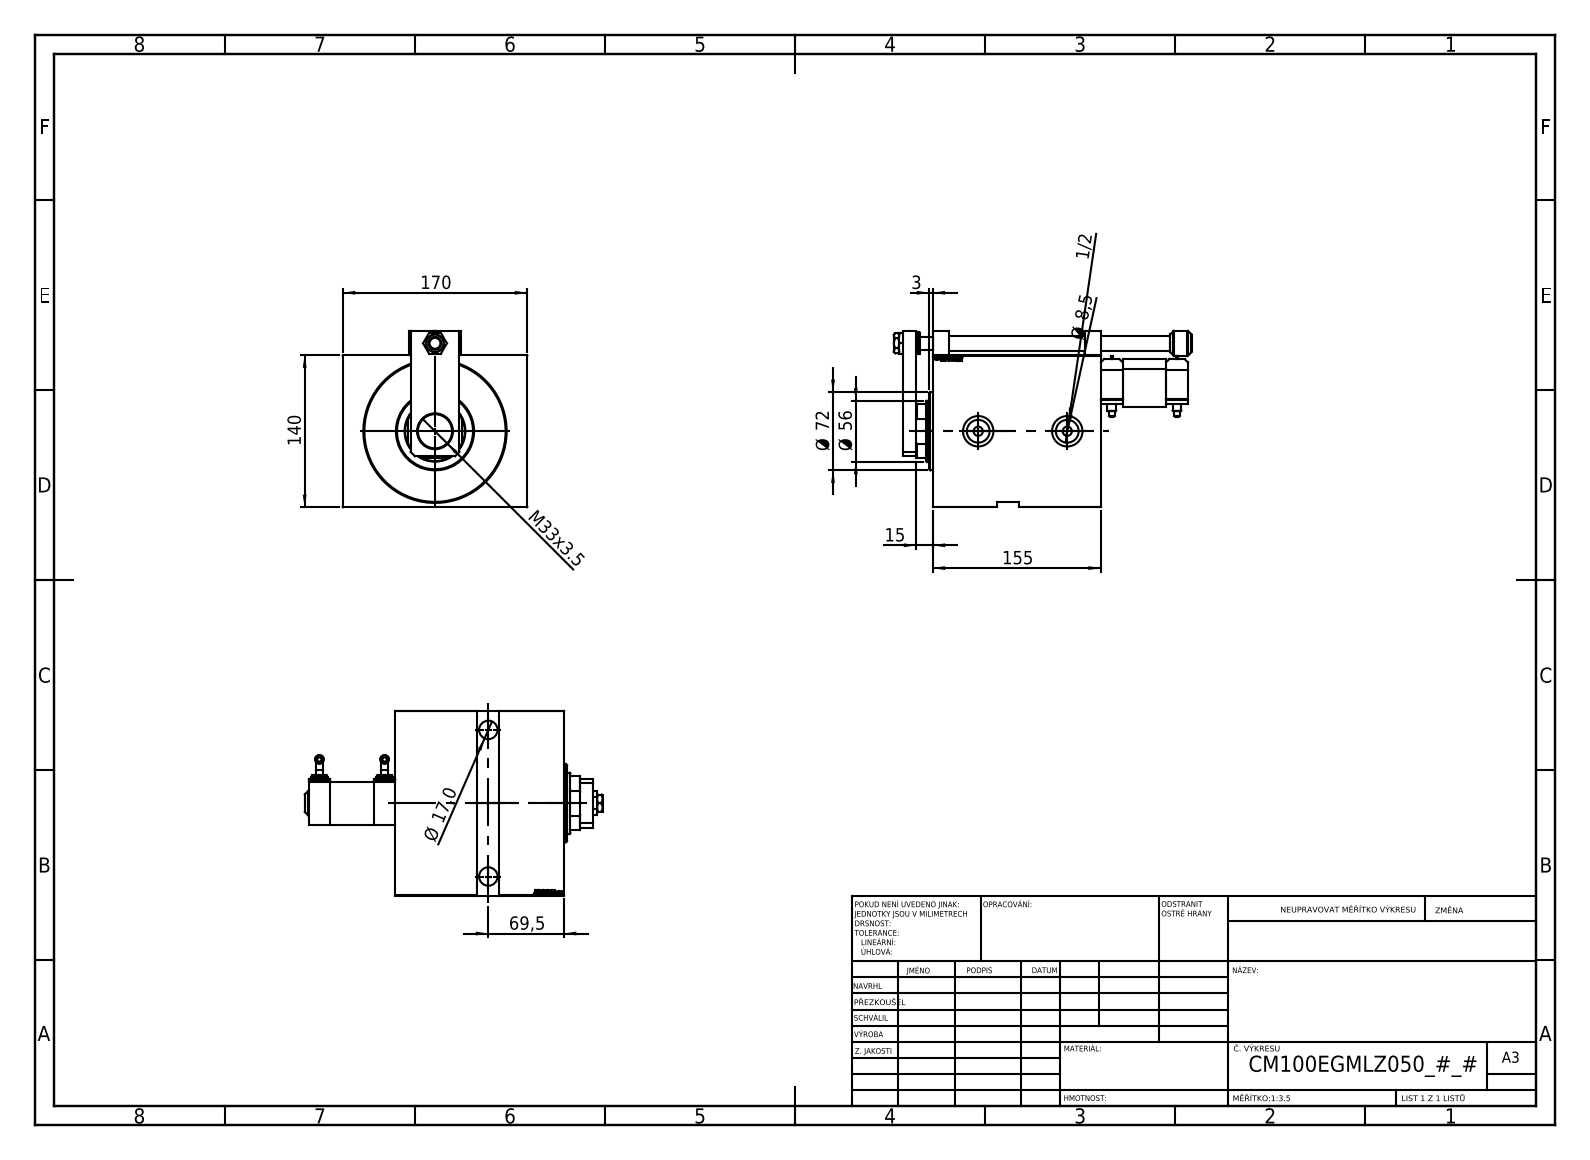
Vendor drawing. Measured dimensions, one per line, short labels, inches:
name: ZARAZKA_P; TYC_P; V450CM_E_Body; NUT_D19_P (+7 more)
written by: SolidWorks 2019 (CONFIG_CONTROL_DESIGN)
unit: in
bodies: 14 solids, 1098 faces (525 planar, 108 cylindrical, 465 other)
size: 10.799 × 6.693 × 6.398
volume: 219 in³; area: 547.6 in²
holes: 4× ⌀0.157, 4× ⌀0.315, 2× ⌀0.335, 2× ⌀0.669, 2× ⌀0.825, 2× ⌀0.984, 2× ⌀1.102, 1× ⌀0.472, 1× ⌀0.512, 1× ⌀0.551, 1× ⌀1.24, 1× ⌀1.299
bosses: 3× ⌀0.787, 2× ⌀0.63, 2× ⌀0.551, 2× ⌀0.315, 2× ⌀0.236, 2× ⌀0.198, 1× ⌀4.016, 1× ⌀2.835
rounds: 1× R0.118, 1× R1.083
face distances: 6.693, 5.512, 6.102, 1.024, 5.079, 0.197, 5.906, 0.787, 4.882, 2.362
hole spacings: 0.787, 3.329, 3.815, 3.907, 4.329, 5.512, 5.568, 3.189
